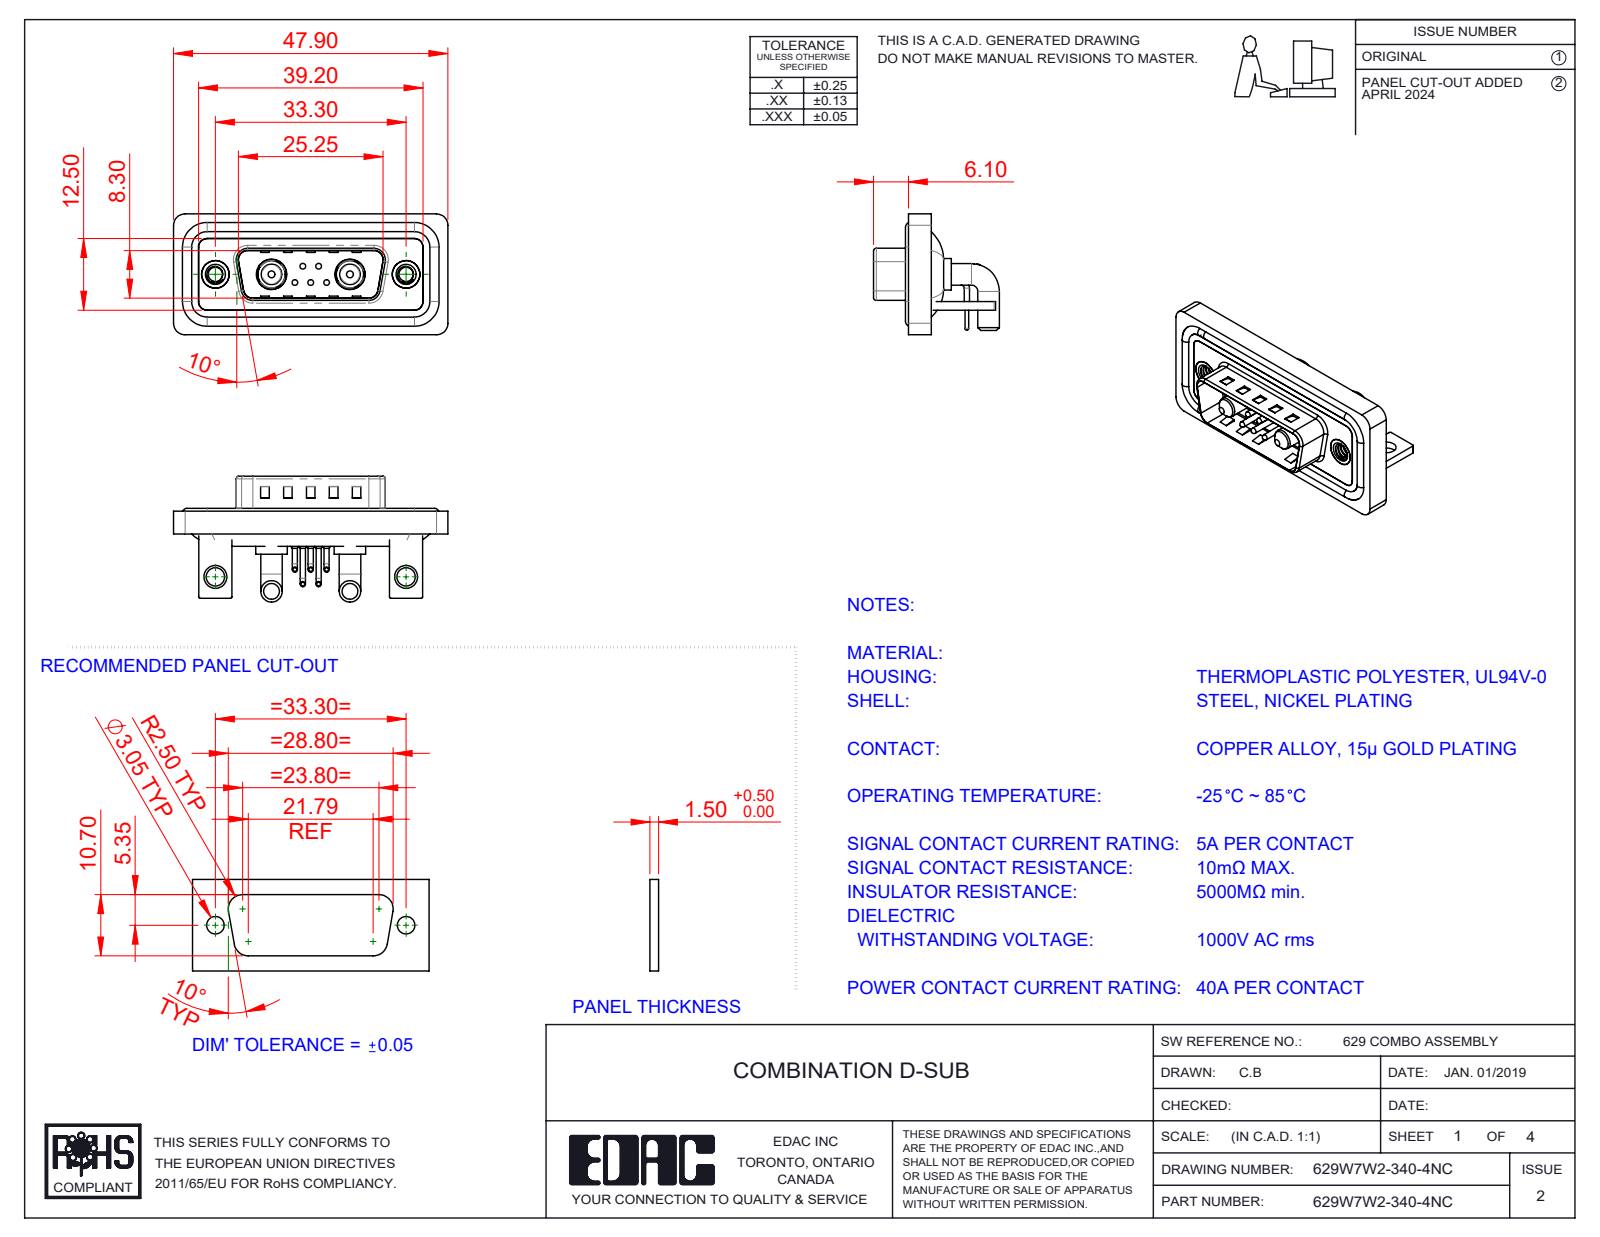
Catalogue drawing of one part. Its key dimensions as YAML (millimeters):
part_name: "629Combo Stabilizer Bracket; 629Combo Shell Rear_15 Contacts; 629Combo Shell Front_15 Contacts; 629Combo Contact Row 1 (+6 more)"
step_written_by: "SolidWorks 2023 (CONFIG_CONTROL_DESIGN)"
units: millimeters
bodies: {solids: 18, faces: 1121, planar: 537, cylindrical: 424, other: 160}
overall_size: [47.9, 21.98, 21.1]
volume: 6098
surface_area: 9817
round_holes:
  - {diameter: 0.75, count: 5}
  - {diameter: 1.6, count: 5}
  - {diameter: 2, count: 5}
  - {diameter: 2.5, count: 2}
  - {diameter: 3.2, count: 2}
  - {diameter: 4, count: 2}
  - {diameter: 4.8, count: 2}
  - {diameter: 4.85, count: 2}
  - {diameter: 5, count: 2}
  - {diameter: 5.3, count: 2}
round_bosses_or_shafts:
  - {diameter: 0.9, count: 10}
  - {diameter: 1.5, count: 5}
  - {diameter: 1, count: 5}
  - {diameter: 0.65, count: 5}
  - {diameter: 3.75, count: 4}
  - {diameter: 1.6, count: 4}
  - {diameter: 5.5, count: 2}
  - {diameter: 5.2, count: 2}
partial_cylinders:
  - {radius: 2, count: 21}
  - {radius: 1.5, count: 18}
  - {radius: 0.25, count: 16}
  - {radius: 0.5, count: 9}
  - {radius: 1.6, count: 8}
  - {radius: 1.01, count: 5}
  - {radius: 0.6, count: 4}
  - {radius: 0.65, count: 4}
face_to_face_distances: [0.4, 1.5, 0.8, 2.9, 2.1, 1.1, 1.6, 1.2, 3.7, 4.5]
hole_center_spacings: [3.16, 2.77, 9.8, 23.5, 33.3, 4.31, 4.33, 5.03]
